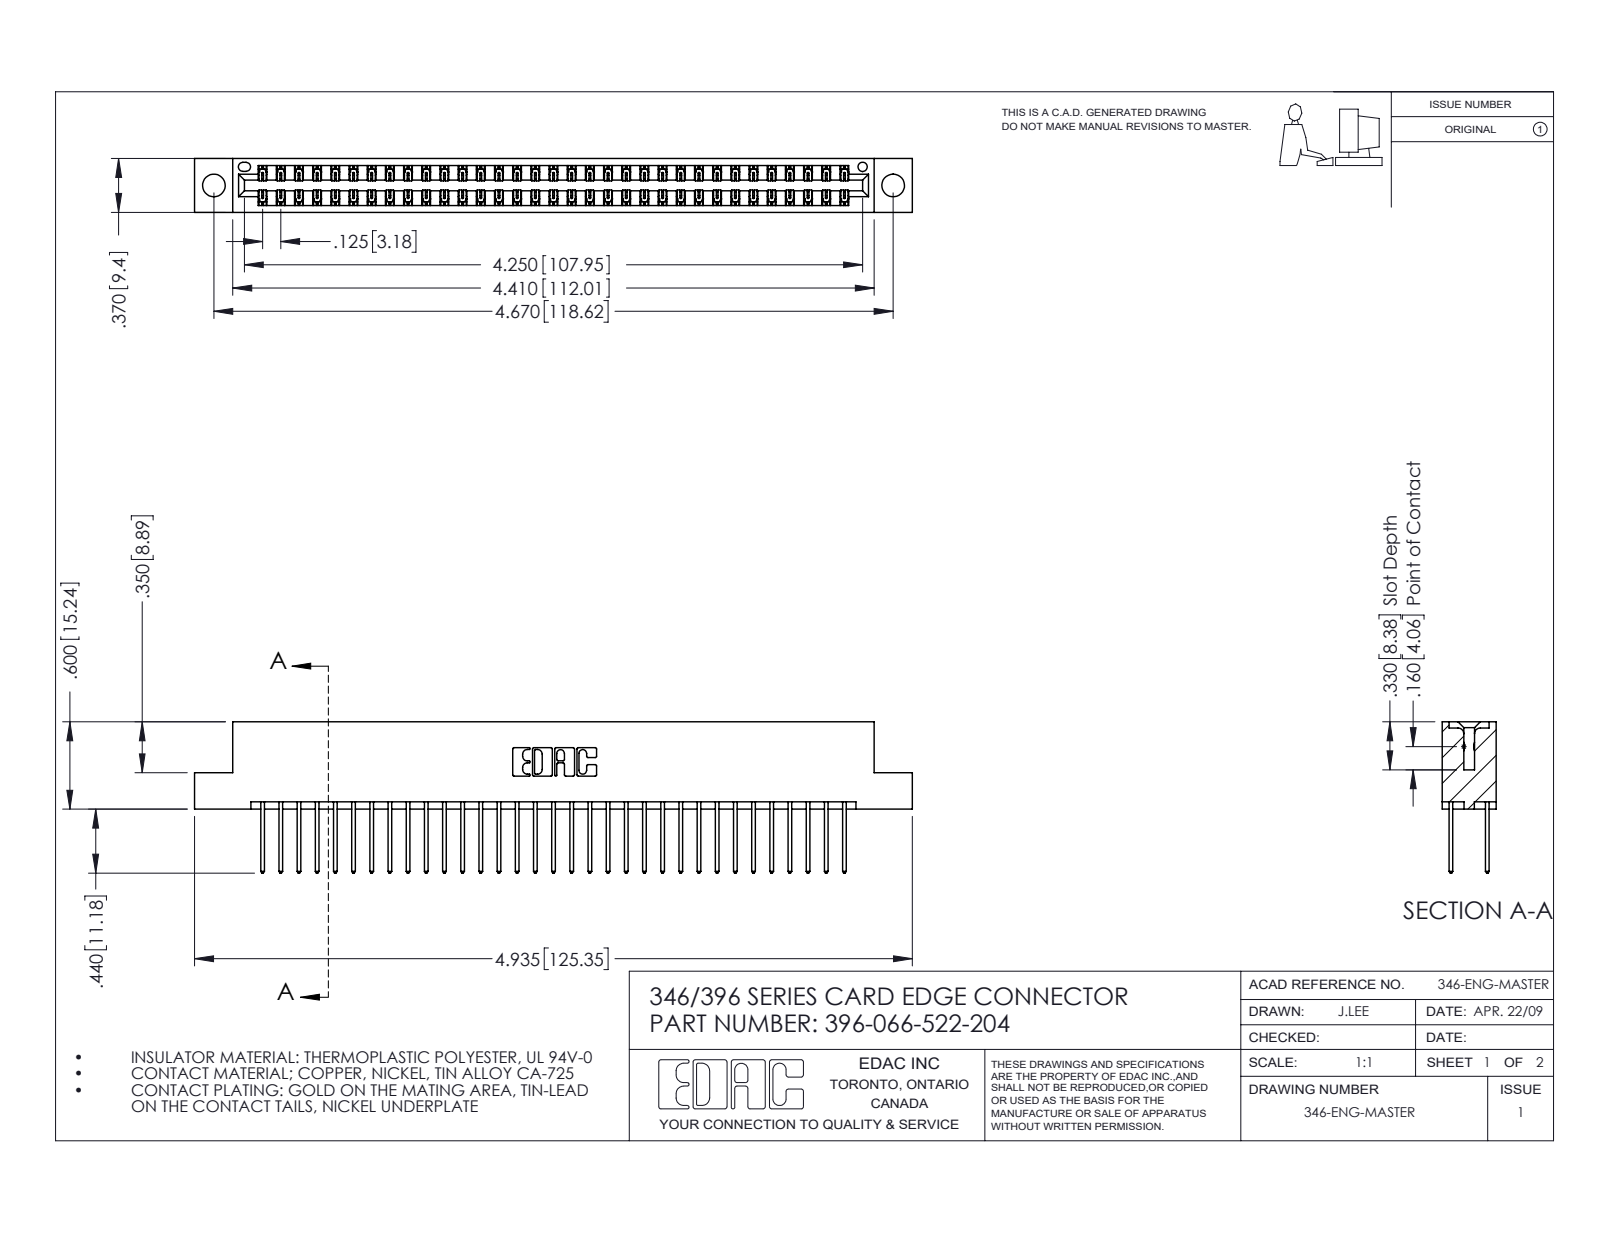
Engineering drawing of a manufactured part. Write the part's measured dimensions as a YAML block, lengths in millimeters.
part_name: "345-292-001_345-293-122; 346 Part_Flush Mounting Lugs - 0.156 Dia-TH; 396-066-522-204"
step_written_by: "SolidWorks 2016 (CONFIG_CONTROL_DESIGN)"
units: millimeters
bodies: {solids: 67, faces: 3554, planar: 2386, cylindrical: 1168, other: 0}
overall_size: [125.3, 26.4, 9.4]
volume: 12200
surface_area: 17270
round_holes:
  - {diameter: 4, count: 2}
  - {diameter: 1.6, count: 1}
partial_cylinders:
  - {radius: 0.2, count: 99}
  - {radius: 0.3, count: 66}
  - {radius: 0.3, count: 22}
  - {radius: 0.2, count: 6}
  - {radius: 0.8, count: 6}
  - {radius: 0.7, count: 3}
  - {radius: 0.4, count: 2}
  - {radius: 0.6, count: 2}
face_to_face_distances: [1.2, 8.2, 6.4, 9.4, 1.8, 7.6, 0.6, 7, 3.8, 5.6]
hole_center_spacings: [6.2, 113.3, 118.6]
